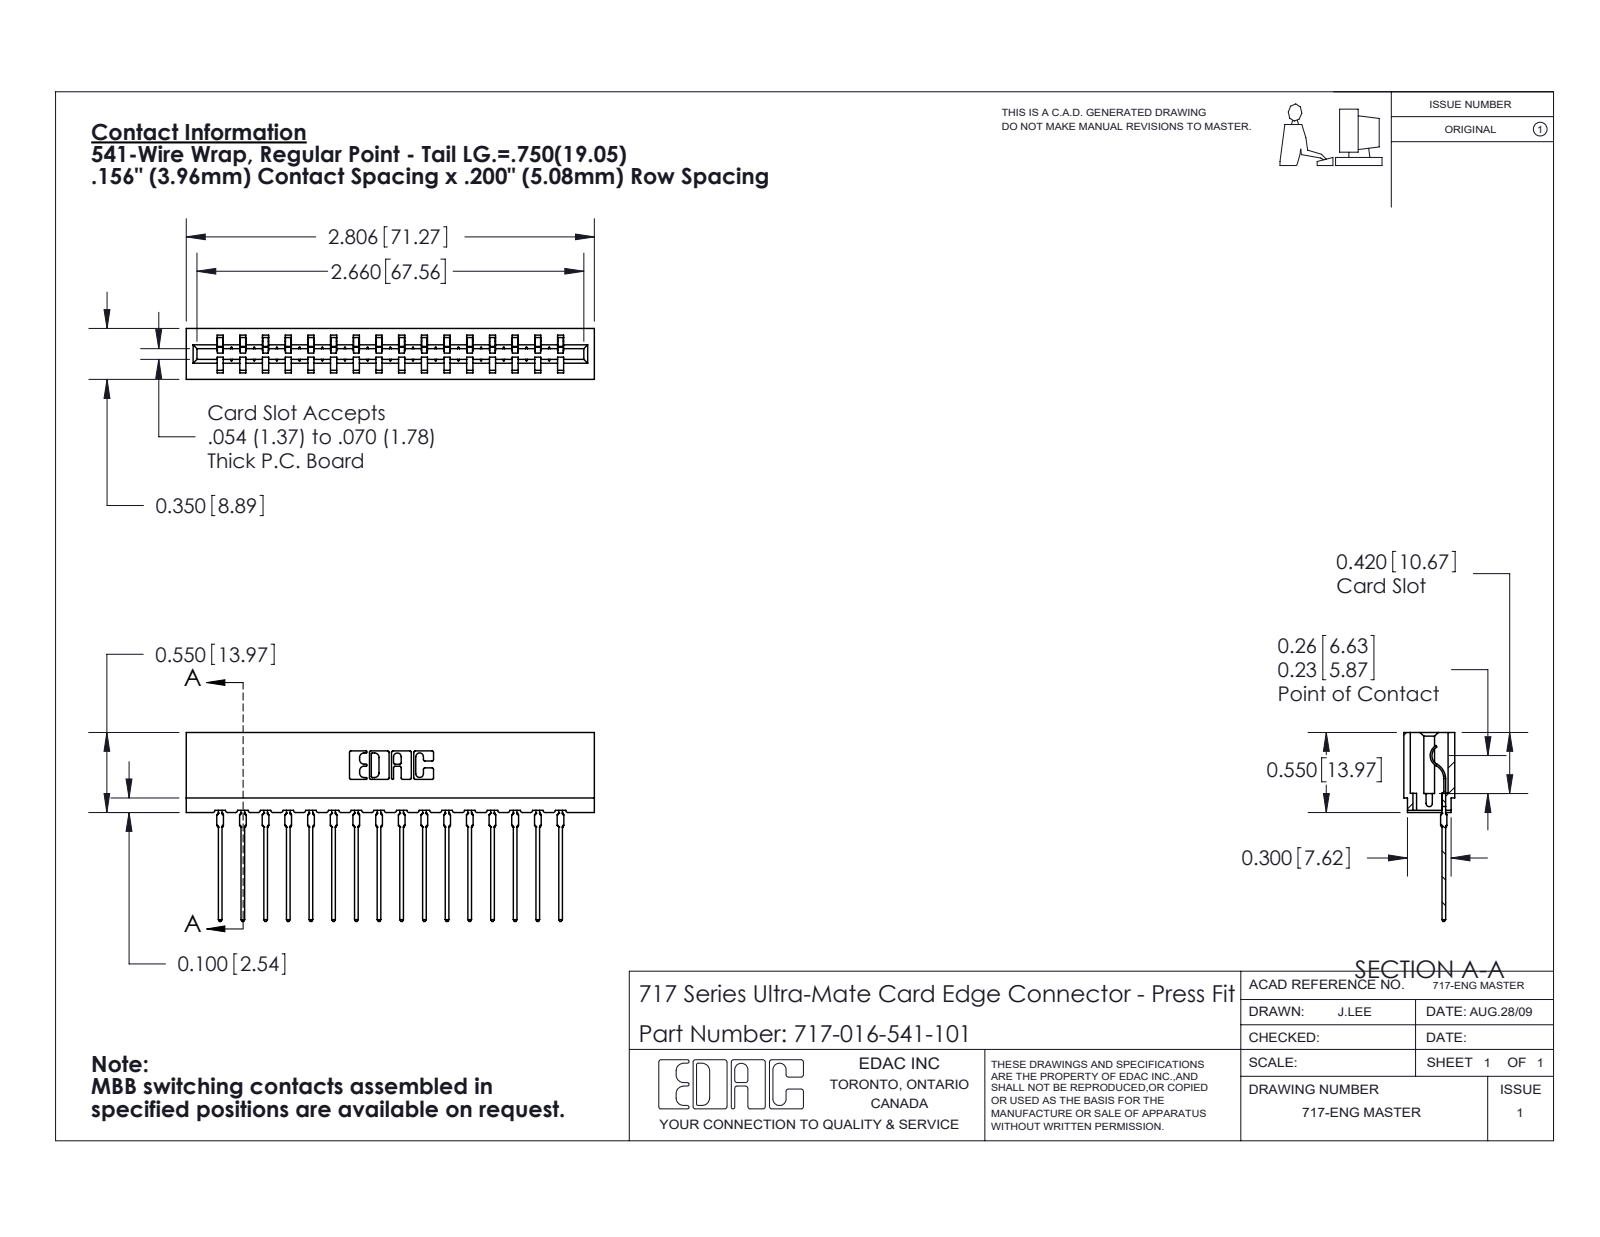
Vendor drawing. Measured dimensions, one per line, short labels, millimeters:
name: 745-292-001_541; 717 Part_Insulator Option - 06; 717-016-541-101
written by: SolidWorks 2020 (CONFIG_CONTROL_DESIGN)
unit: mm
bodies: 17 solids, 1902 faces (1142 planar, 344 cylindrical, 416 other)
size: 71.3 × 33 × 8.9
volume: 6 210 mm³; area: 8 768 mm²
rounds: 32× R0.4, 32× R0.5, 22× R0.3, 6× R0.2, 6× R0.8, 4× R0.1, 4× R0.3, 3× R0.7
face distances: 5.4, 3.5, 8.9, 4, 11.9, 15.8, 5, 7.9, 1.9, 1.6
